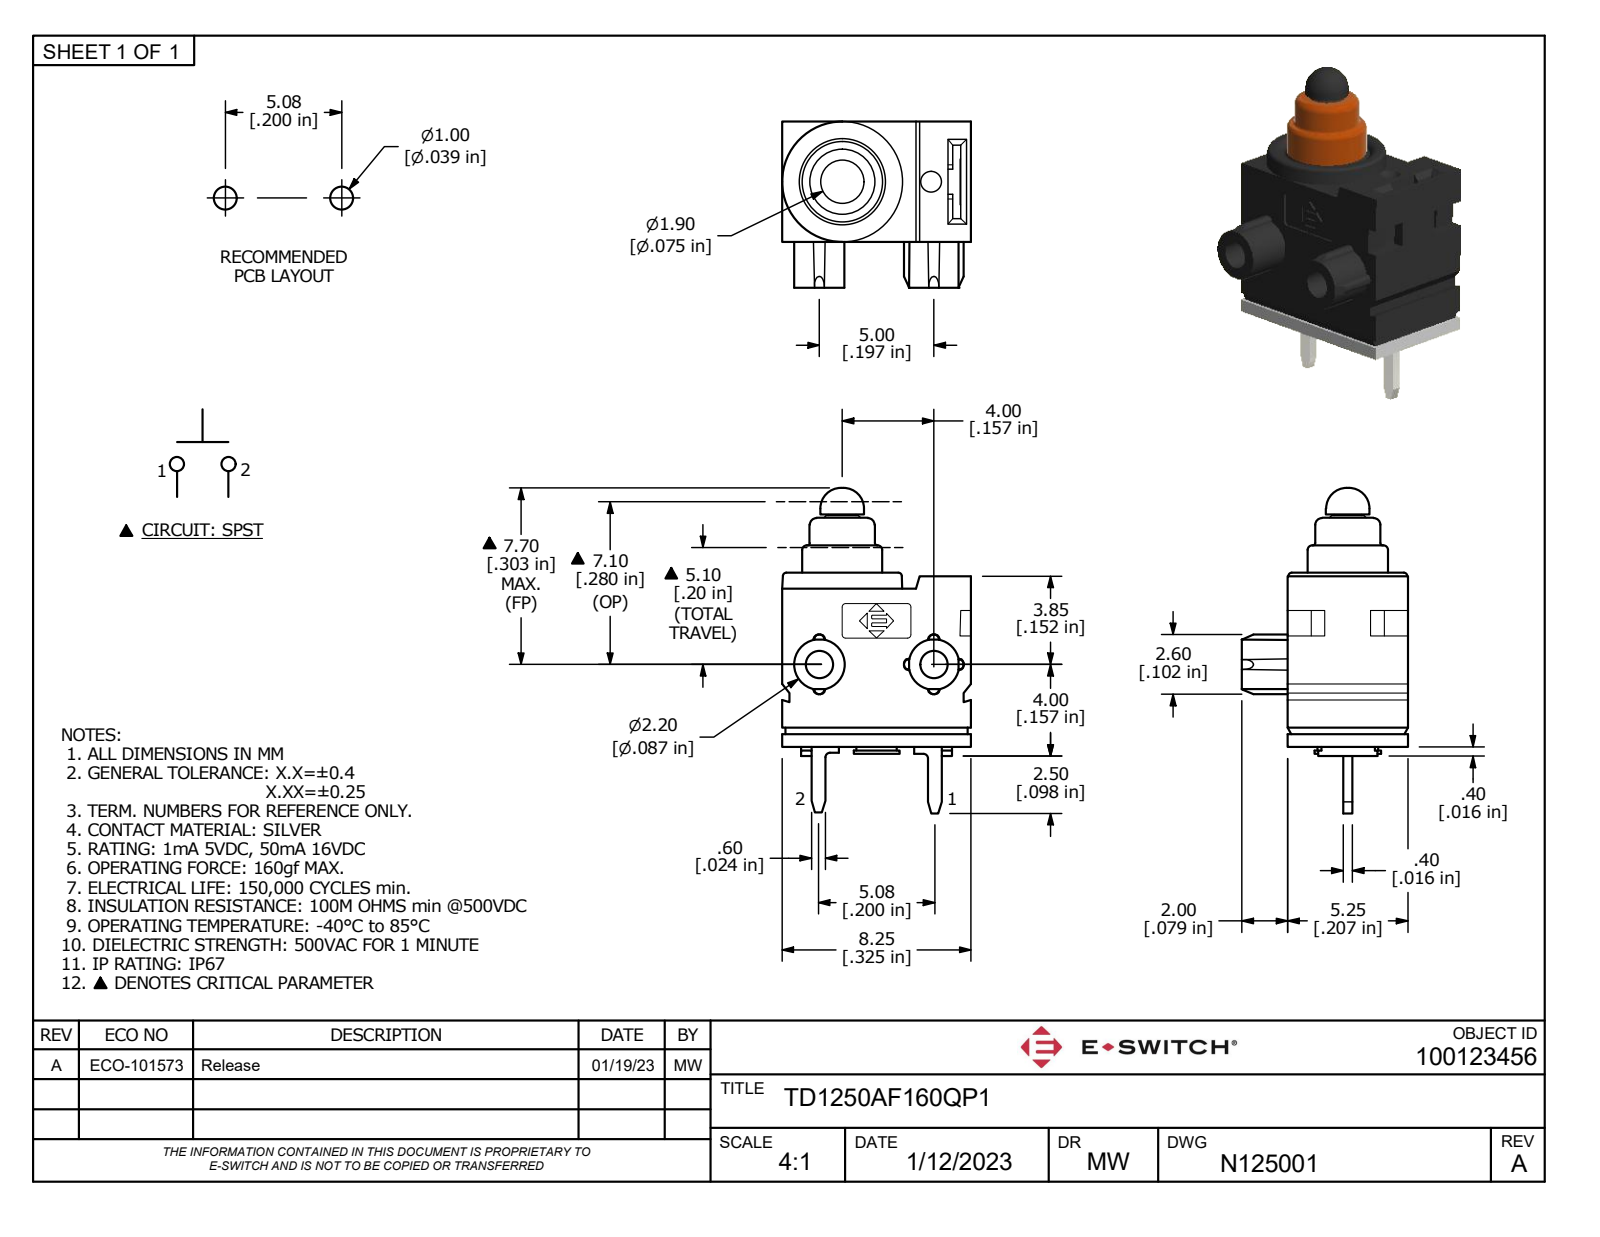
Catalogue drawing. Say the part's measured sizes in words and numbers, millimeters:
The part is named "TD1250AF160QP1". Its 3-D file was written by "Autodesk Inventor 2022 (AUTOMOTIVE_DESIGN)". It is 1 solid with 223 faces: 171 planar, 40 cylindrical and 12 other. Overall it measures 14.2 by 8.25 by 7.25 millimeters. Its volume is 348 cubic millimeters and its surface area 440 square millimeters. Round holes: 2 of diameter 1.2, 1 of diameter 4.65. Round bosses or shafts: 1 of diameter 4.5, 1 of diameter 3.5, 1 of diameter 2.85, 1 of diameter 2.2, 1 of diameter 1.9, 1 of diameter 1.2. Partial cylindrical surfaces (rounded edges, fillets, slot ends): 14 of radius 0.2, 4 of radius 0.15, 1 of radius 1.1. The main face-to-face distances are 5.24, 8.24, 0.55, 6.9, 7.45, 7.24, 7.75, 0.45, 2.42, 2.82. The hole center spacings are 5.
